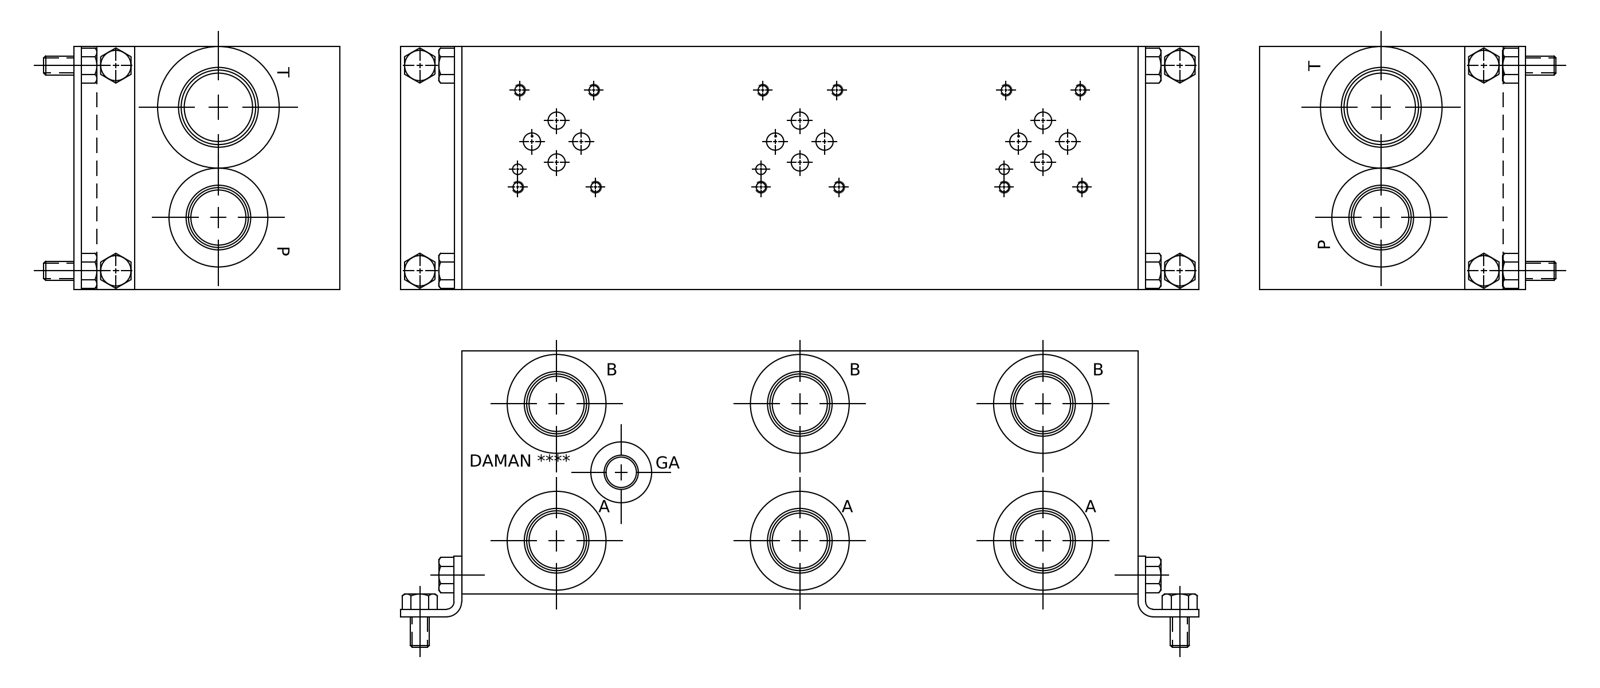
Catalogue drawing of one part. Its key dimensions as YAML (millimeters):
part_name: "Part_AD03HP034S_3D"
step_written_by: "Autodesk Inventor 2020 (AUTOMOTIVE_DESIGN)"
units: millimeters
bodies: {solids: 1, faces: 760, planar: 409, cylindrical: 102, other: 249}
overall_size: [282.57, 101.6, 101.6]
volume: 2704000
surface_area: 168894
round_holes:
  - {diameter: 3.78, count: 12}
  - {diameter: 4.83, count: 12}
  - {diameter: 6.35, count: 9}
  - {diameter: 23.01, count: 7}
  - {diameter: 24.92, count: 7}
  - {diameter: 27.43, count: 7}
  - {diameter: 42.04, count: 7}
  - {diameter: 26.99, count: 5}
  - {diameter: 3.96, count: 3}
  - {diameter: 7.14, count: 3}
  - {diameter: 6.53, count: 2}
  - {diameter: 7.92, count: 2}
face_to_face_distances: [101.6, 282.57, 0.79, 100.81, 281.79, 0.78, 281, 281.78, 19.05, 19.84]
hole_center_spacings: [101.6, 203.2, 13.52, 13.54, 22.05, 33.55, 40.5, 51.45]
